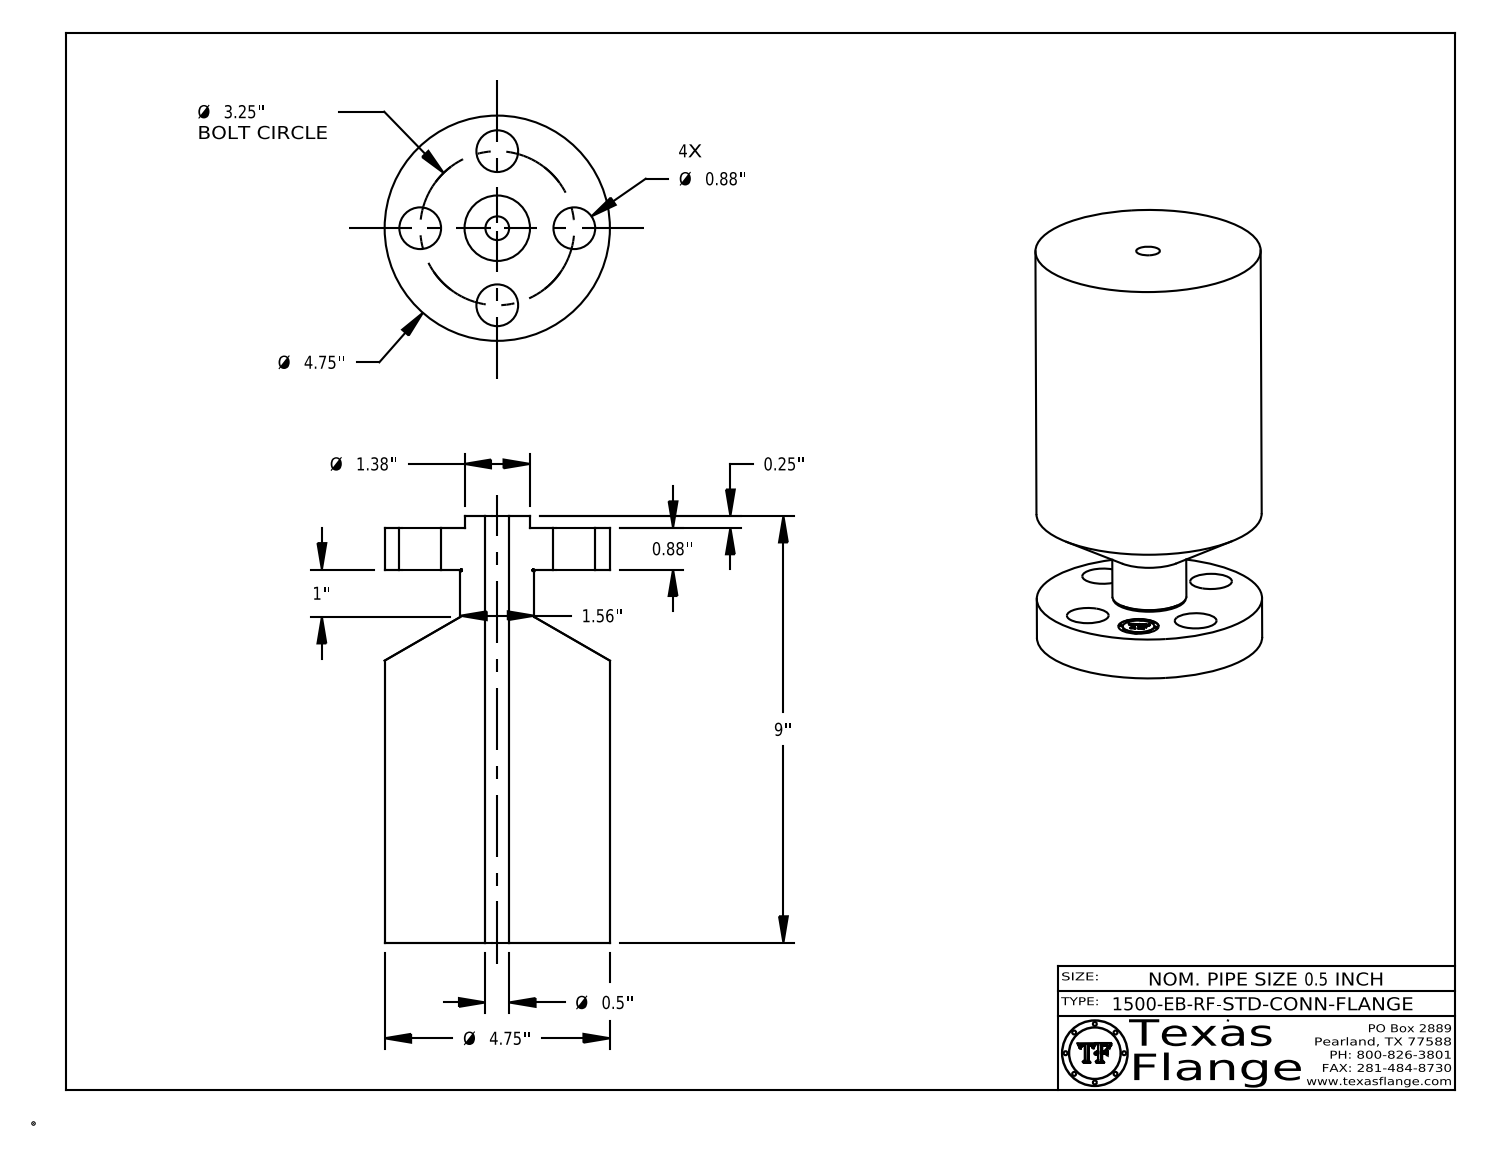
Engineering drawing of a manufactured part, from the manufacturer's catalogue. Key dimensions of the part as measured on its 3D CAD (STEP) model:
Part name (STEP PRODUCT): 0.5-1500-EB-RF-STD-CONN-FLANGE
STEP written by: CATIA V5 STEP AP214 (AUTOMOTIVE_DESIGN)
Units: inches
Bodies: 1 solid, 413 faces (369 planar, 38 cylindrical, 6 other)
Overall size (bounding box): 9 × 4.75 × 4.75
Volume: 127.2 in³ · Surface area: 196.2 in²
Round holes (diameter × count): ⌀0.88 ×4, ⌀0.5 ×1, ⌀0.85 ×1
Round bosses / shafts (diameter × count): ⌀0.051 ×8, ⌀4.75 ×1, ⌀1.56 ×1, ⌀1.38 ×1, ⌀0.67 ×1
Main face-to-face distances: 8.75, 0.88, 7.87, 0.25, 1.13, 9, 1.125, 0.875, 7.875, 0.254
Hole centre spacings: 1.625, 2.298, 1.244, 3.003, 3.25
